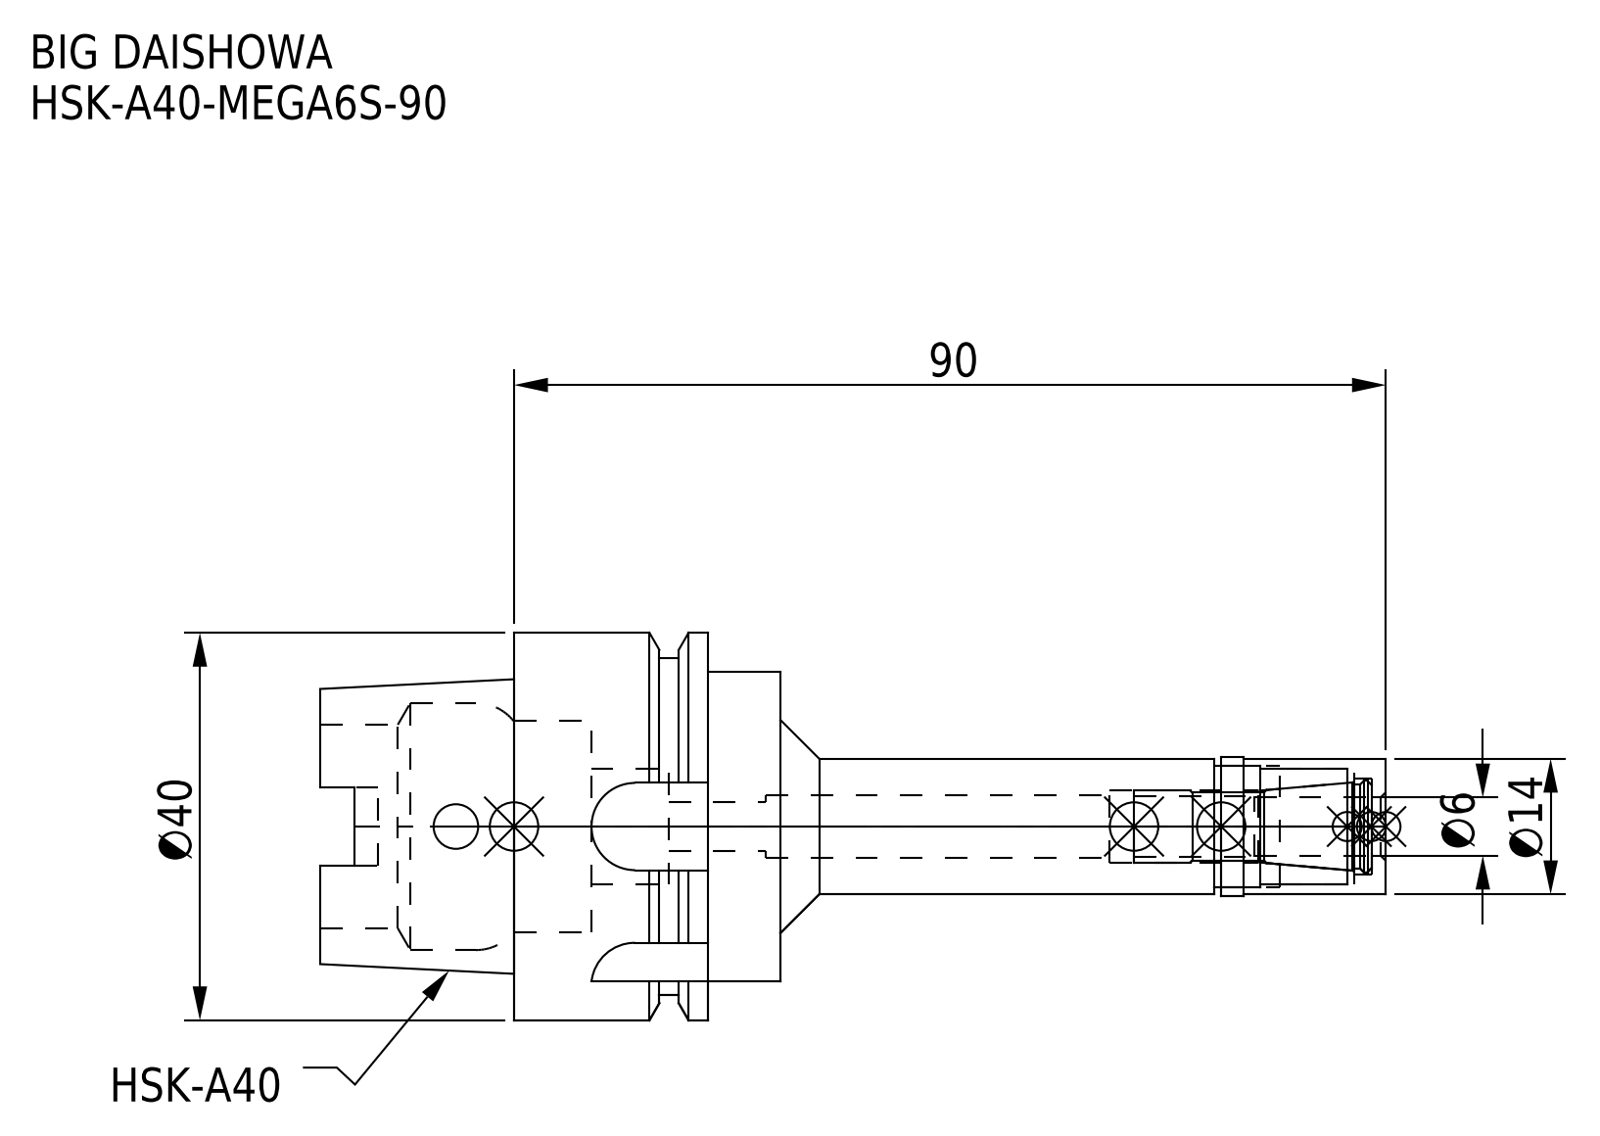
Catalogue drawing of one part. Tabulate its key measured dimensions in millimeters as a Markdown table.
| quantity | value |
| --- | --- |
| part name | HSK-A40-MEGA6S-90-060.stp; HSK-A40-MEGA6S-90_1.stp; MGN6S_1.stp; HSK-A40-MEGA6S-90 (+3 more) |
| STEP written by | SolidWorks 2019 (CONFIG_CONTROL_DESIGN) |
| units | millimeters |
| bodies | 2 solids, 123 faces (47 planar, 56 cylindrical, 20 other) |
| overall size | 110 × 40 × 40 |
| volume | 37 725 mm³ |
| surface area | 15 700 mm² |
| round holes (diameter × count) | 4.6 × 1, 5 × 1, 6.1 × 1, 6.4 × 1, 7.4 × 1, 10 × 1, 12 × 1, 12.5 × 1, 21 × 1, 21.8 × 1, 25.5 × 1 |
| round bosses / shafts (diameter × count) | 40 × 1, 34.8 × 1, 32 × 1, 14.3 × 1, 14 × 1 |
| partial cylindrical surfaces (radius × count) | 1.88 × 4, 4.5 × 4 |
| main face-to-face distances | 20, 27.5, 7.5, 19.55, 12.05, 7.95, 40, 47.5, 27.95, 34 |
